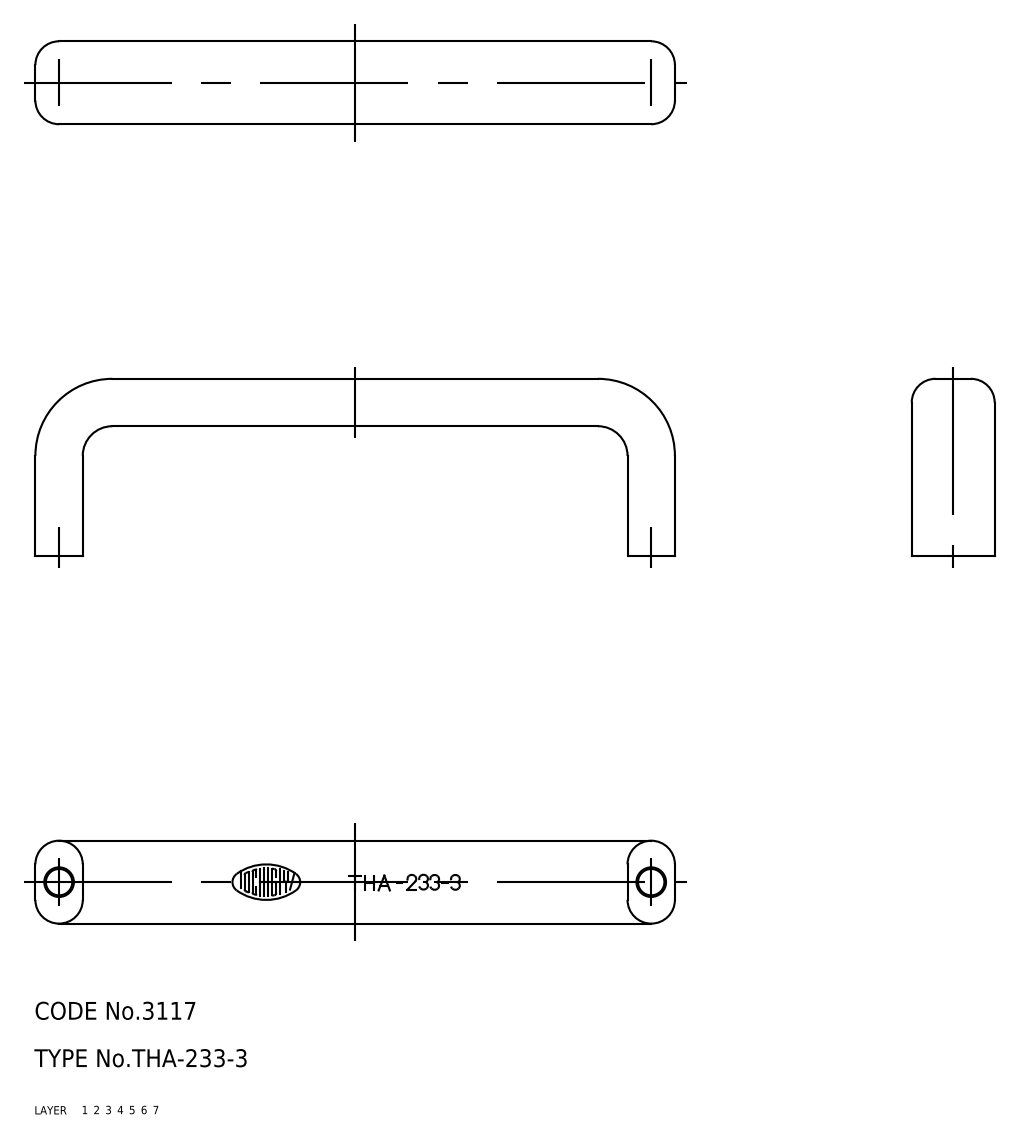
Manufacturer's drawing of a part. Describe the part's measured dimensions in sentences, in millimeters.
The part is named "pull". Its 3-D file was written by "CADfix (AUTOMOTIVE_DESIGN)". It is 1 solid with 28 faces: 0 planar, 0 cylindrical and 28 other. Overall it measures 108 by 30 by 14 millimeters. Its volume is 13 784 cubic millimeters and its surface area 5 869 square millimeters.
